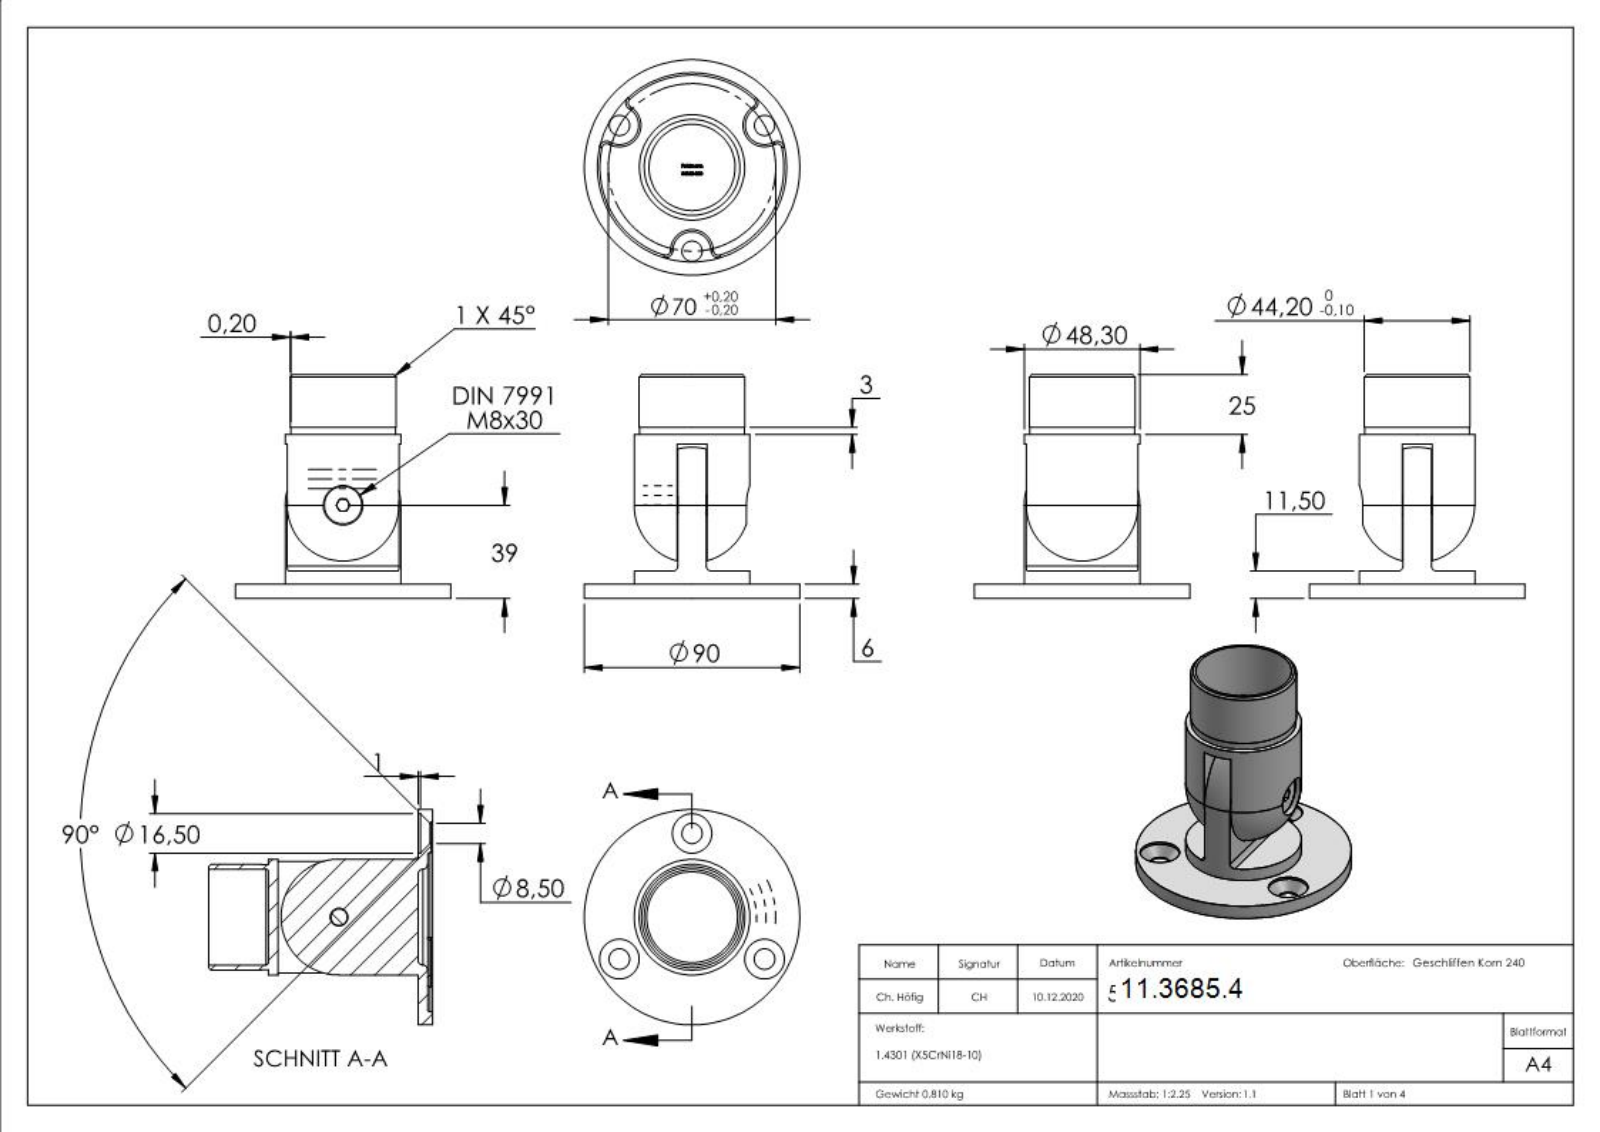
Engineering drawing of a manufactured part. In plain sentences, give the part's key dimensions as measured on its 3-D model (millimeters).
The part is named "socket countersunk head screw_din_DIN 7991 - M8 x 30 --- 30S; 5624X-320 Teil2_56242-320 Teil2; 5624X-320 Teil1; socket countersunk head screw_din (+3 more)". Its 3-D file was written by "SolidWorks 2018 (CONFIG_CONTROL_DESIGN)". It is 3 solids with 627 faces: 183 planar, 155 cylindrical and 289 other. Overall it measures 93.5 by 90 by 90 millimeters. Its volume is 103 935 cubic millimeters and its surface area 45 466 square millimeters. Round holes: 4 of diameter 16.5, 3 of diameter 8.5, 2 of diameter 40, 1 of diameter 6.8, 1 of diameter 8.2, 1 of diameter 79. Round bosses or shafts: 1 of diameter 90, 1 of diameter 48.3, 1 of diameter 44.2, 1 of diameter 43.8, 1 of diameter 15.57, 1 of diameter 13, 1 of diameter 8. Partial cylindrical surfaces (rounded edges, fillets, slot ends): 24 of radius 1, 6 of radius 3, 3 of radius 8, 2 of radius 2, 1 of radius 6.25. The main face-to-face distances are 4, 62.5, 12.2, 3.6, 3.9, 8.6, 8.3, 2, 6, 68.5. The hole center spacings are 35, 60.62.
